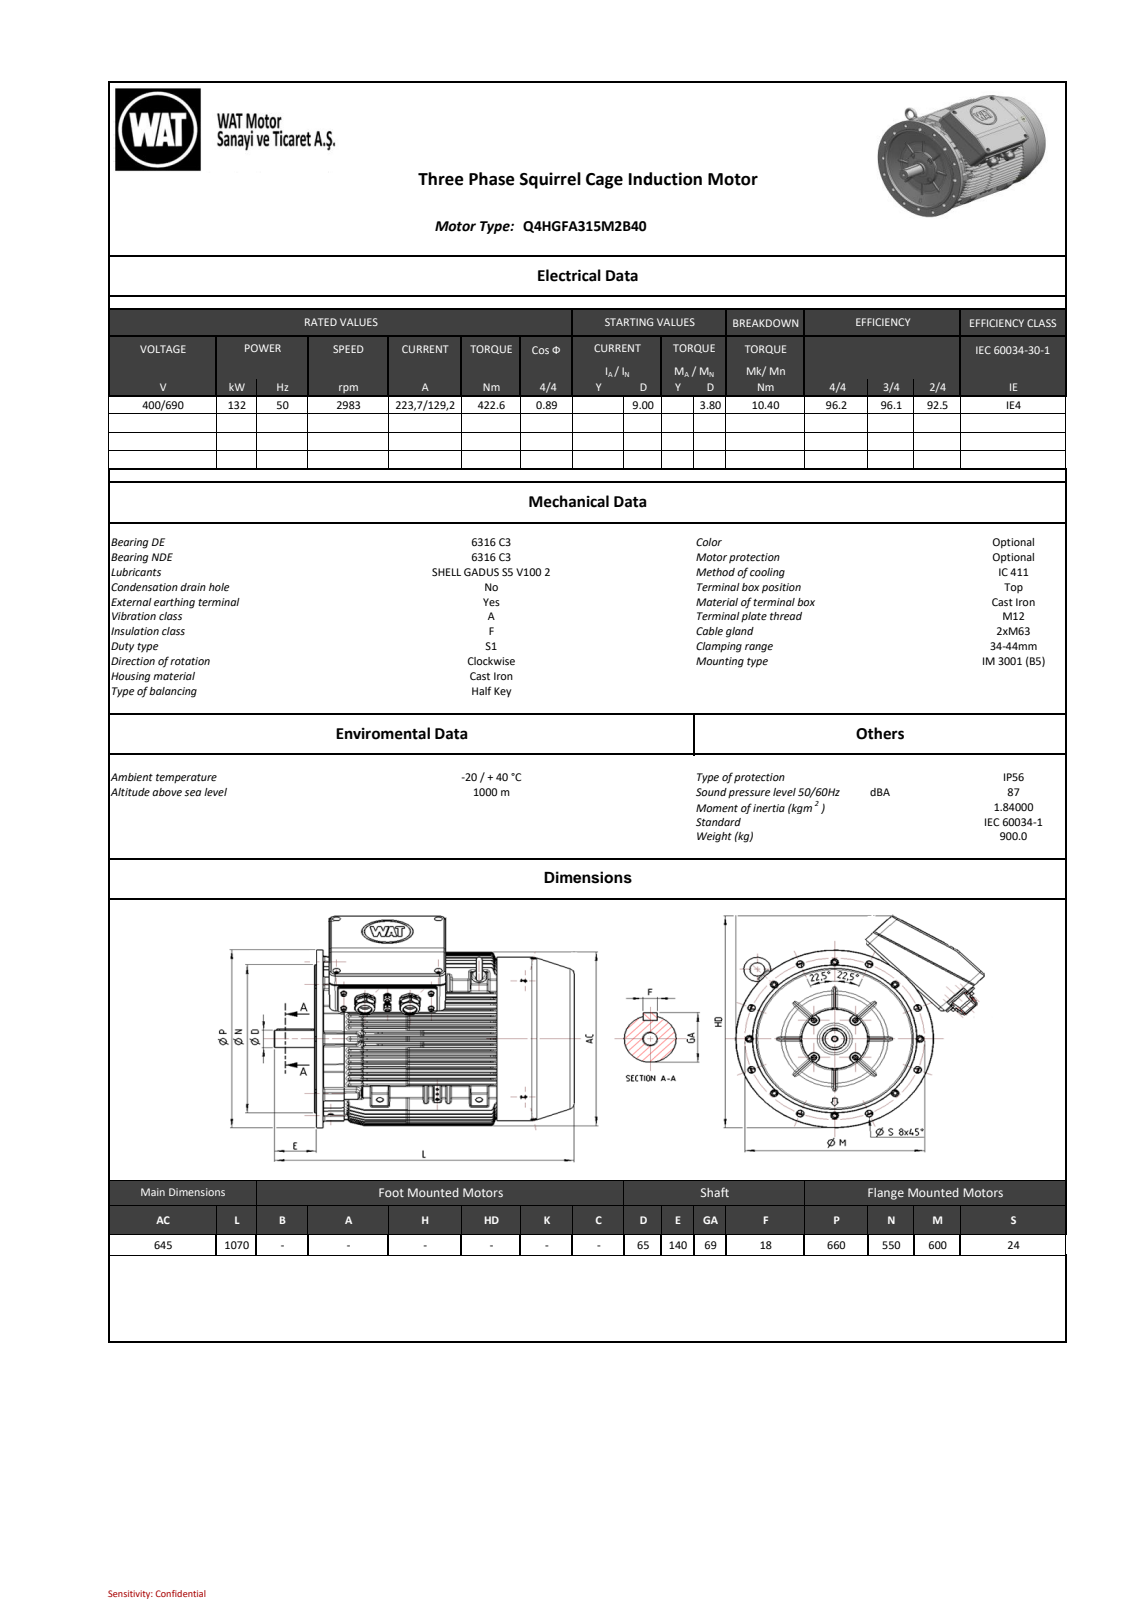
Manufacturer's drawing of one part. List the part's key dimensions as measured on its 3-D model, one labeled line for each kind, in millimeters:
Part name (STEP PRODUCT): 26009910674F4pnc
STEP written by: SIEMENS PLM Software NX 11.0 (AUTOMOTIVE_DESIGN)
Units: millimetres
Bodies: 0 solids, 6042 faces (2705 planar, 1234 cylindrical, 2103 other)
Overall size (bounding box): 1070 × 829.19 × 785.69
Round holes (diameter × count): ⌀24 ×8, ⌀26 ×8, ⌀8.5 ×6, ⌀20 ×5, ⌀8 ×4, ⌀9 ×4, ⌀22 ×4, ⌀4 ×2, ⌀12 ×2, ⌀12.1 ×2, ⌀15 ×2, ⌀18 ×2
Round bosses / shafts (diameter × count): ⌀16 ×8, ⌀20 ×5, ⌀10 ×4, ⌀64.8 ×2, ⌀50 ×2, ⌀660 ×1, ⌀607 ×1, ⌀565 ×1
Partial cylindrical surfaces — rounded edges, fillets, slot ends (radius × count): R6 ×484, R3 ×155, R2.09 ×66, R2.61 ×61, R0.8 ×36, R10 ×30, R0.4 ×24, R1.5 ×14
Main face-to-face distances: 117, 20.71, 305.15, 41.51, 284.35, 20.8, 263.64, 242.48, 83.38, 263.46
Hole centre spacings: 486.48, 79.06, 115.07, 115.08, 218.13, 300, 325.24, 325.26
